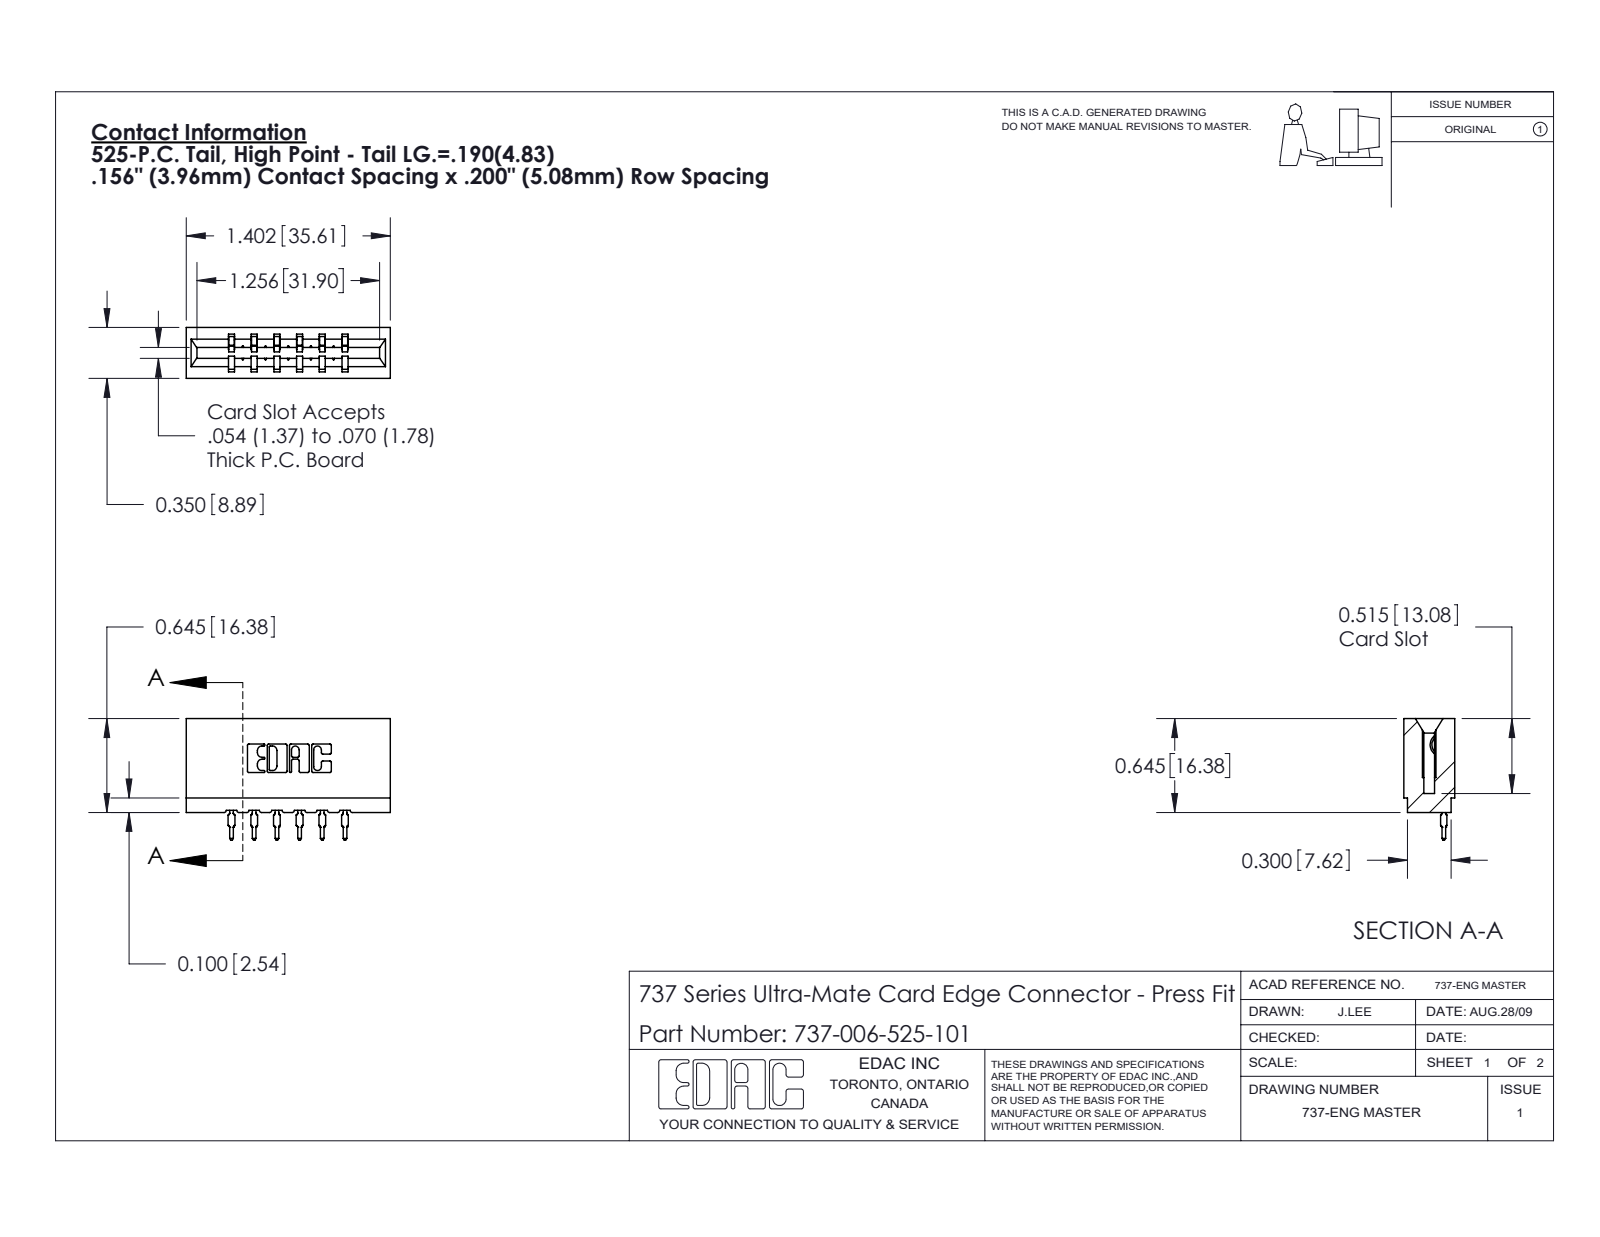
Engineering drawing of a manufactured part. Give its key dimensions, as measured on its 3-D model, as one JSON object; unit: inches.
{"part_name": "737-006-525-101; 745-292-001_525; 737 Part_Insulator Option - 01", "step_written_by": "SolidWorks 2020 (CONFIG_CONTROL_DESIGN)", "units": "inches", "bodies": {"solids": 7, "faces": 772, "planar": 462, "cylindrical": 154, "other": 156}, "overall_size": [1.402, 0.836, 0.35], "volume_in3": 0.225, "surface_area_in2": 6.621, "partial_cylinders_radius": [[0.01, 22], [0.015, 12], [0.021, 12], [0.007, 6], [0.031, 6], [0.005, 4], [0.011, 4], [0.026, 3]], "face_to_face_distances": [0.156, 0.138, 0.212, 0.35, 0.312, 0.354, 0.198, 0.074, 0.468, 0.312]}
